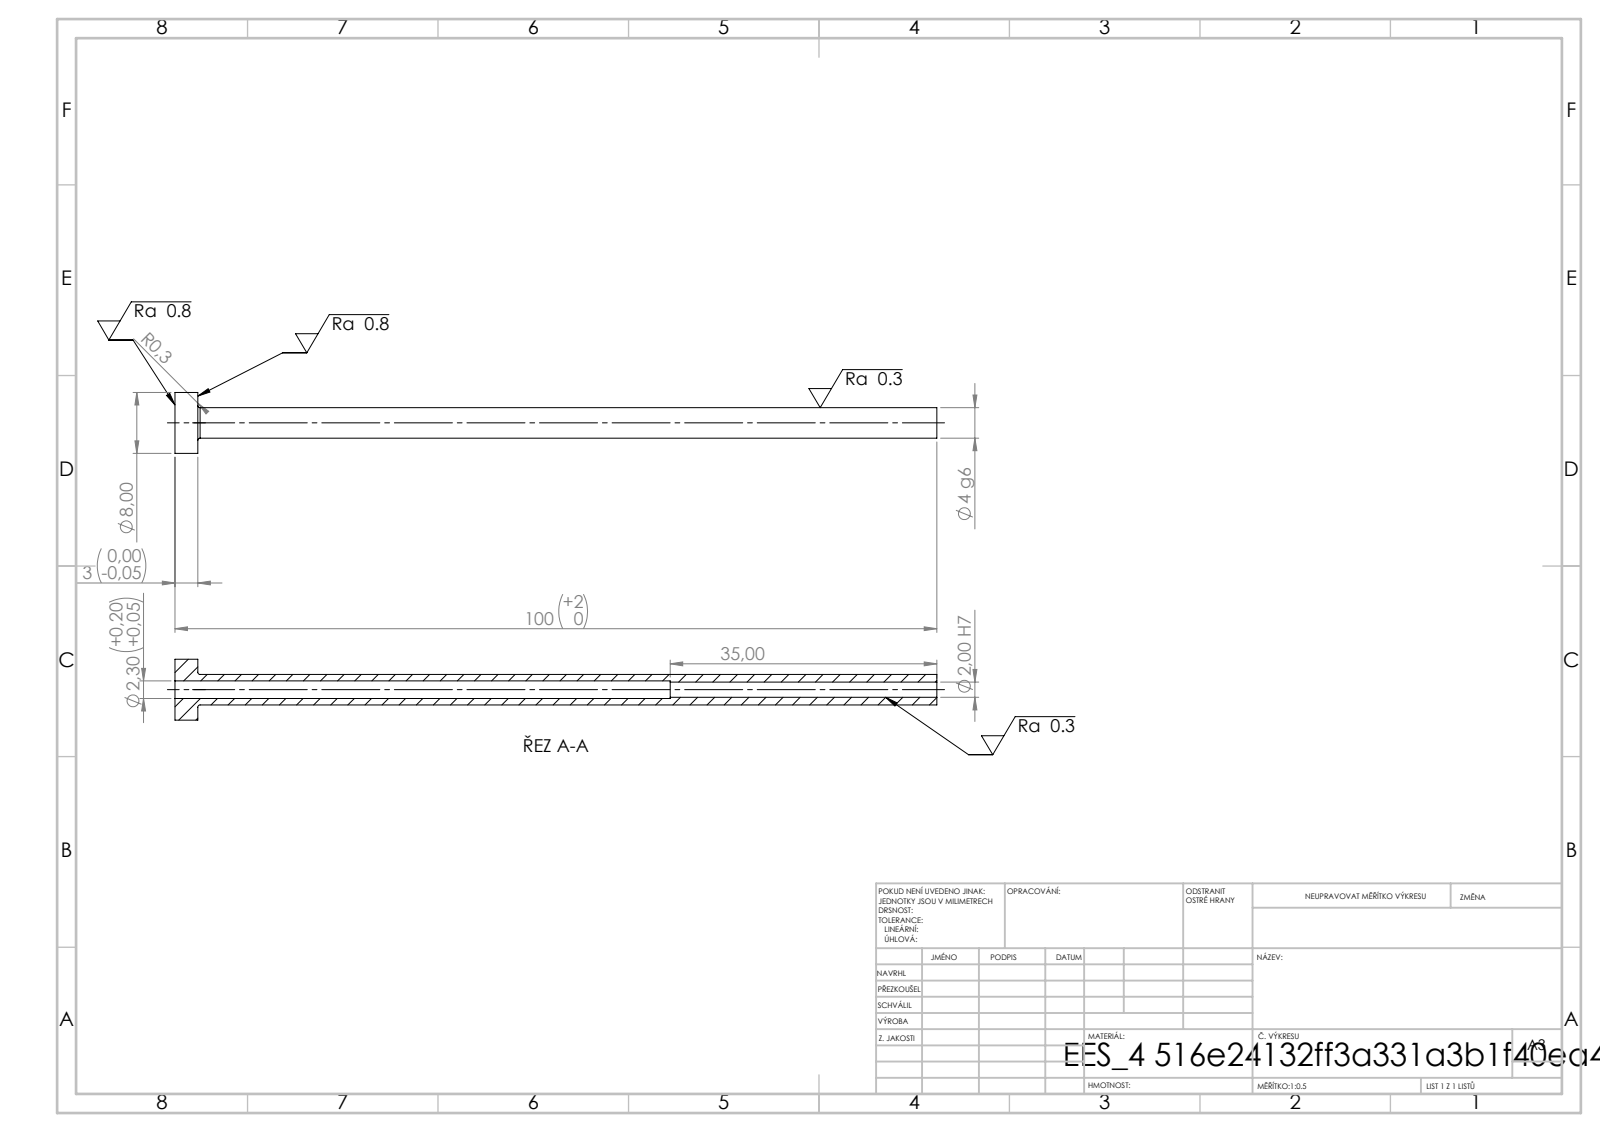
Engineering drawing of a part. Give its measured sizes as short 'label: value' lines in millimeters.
written by: SolidWorks 2019 (CONFIG_CONTROL_DESIGN)
unit: mm
bodies: 1 solid, 14 faces (4 planar, 8 cylindrical, 2 other)
size: 100 × 8 × 8
volume: 990 mm³; area: 2 077 mm²
holes: 1× ⌀2, 1× ⌀2.3
bosses: 1× ⌀8, 1× ⌀4
face distances: 3, 100, 97, 65, 62, 35
